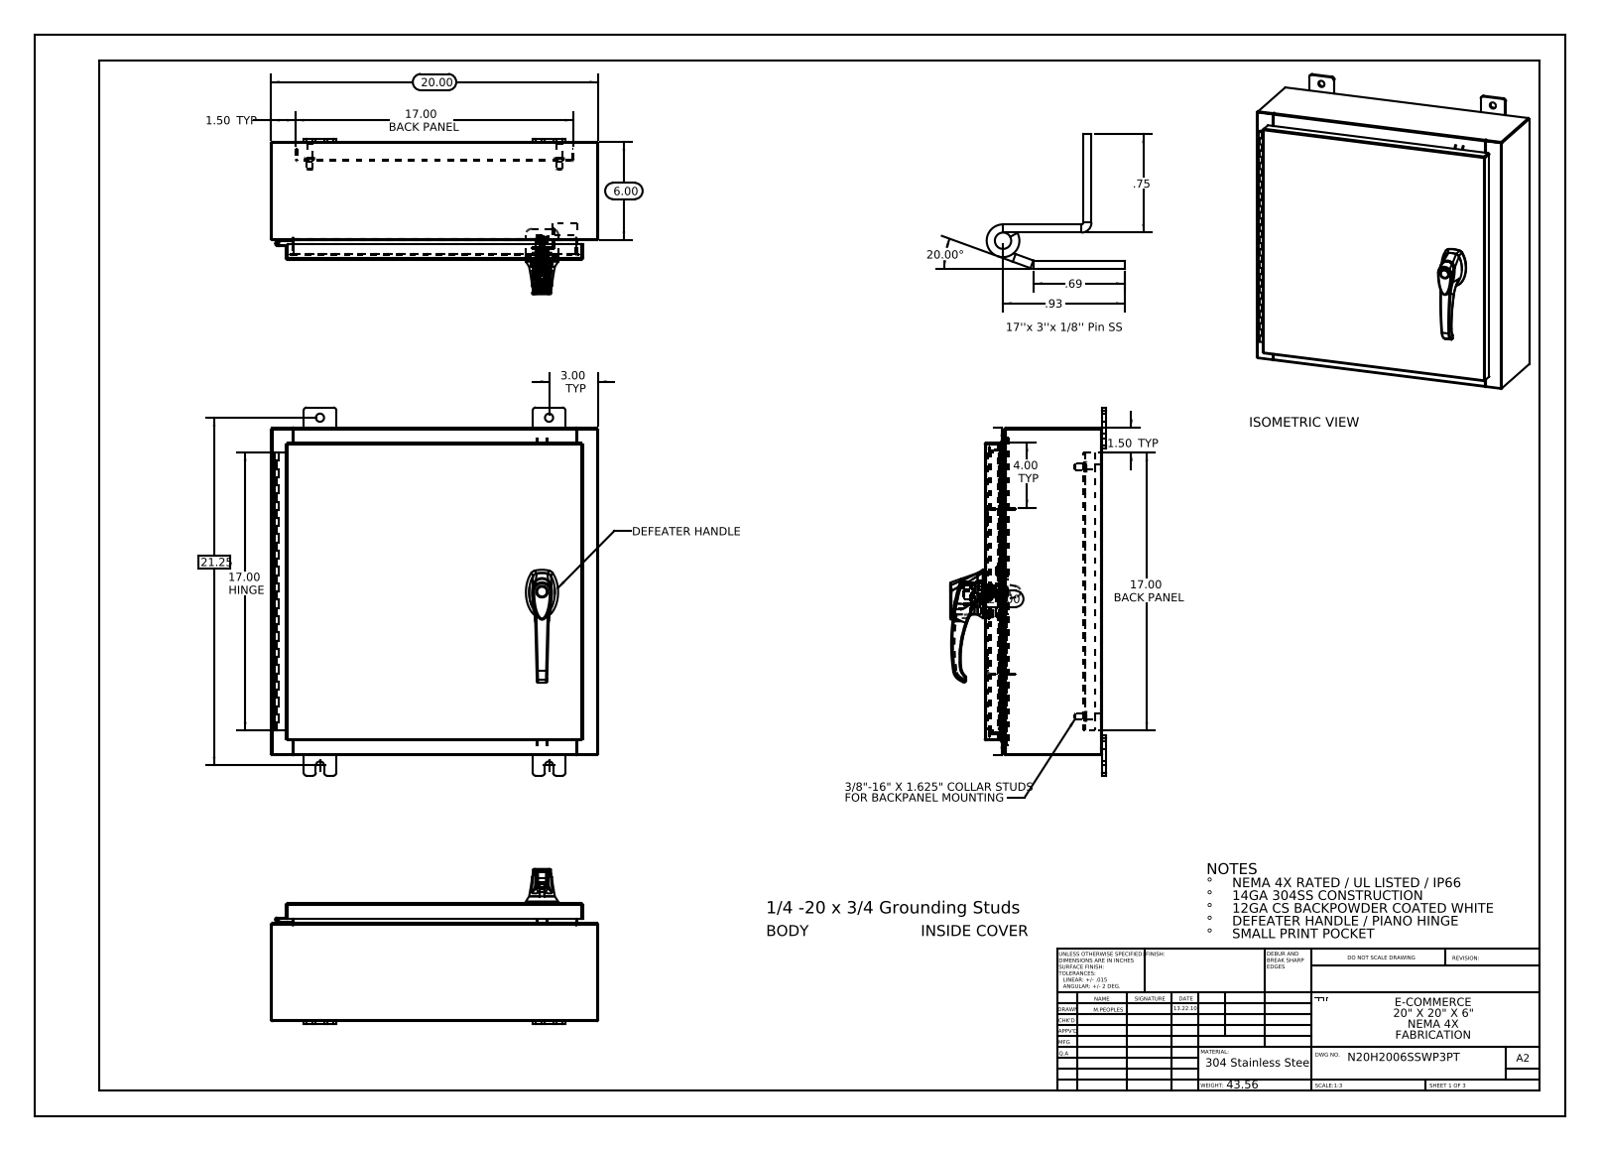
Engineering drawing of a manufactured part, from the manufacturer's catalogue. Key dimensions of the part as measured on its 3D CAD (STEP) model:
Part name (STEP PRODUCT): 297026; 26161102; N20H2006SSWP3PT Defeater Handle Rod; N20H2006SSWP3PT Hinge Enclosure Side2 (+8 more)
STEP written by: SolidWorks 2013 (CONFIG_CONTROL_DESIGN)
Units: inches
Bodies: 31 solids, 2316 faces (817 planar, 845 cylindrical, 654 other)
Overall size (bounding box): 22.5 × 20 × 9.495
Volume: 155.7 in³ · Surface area: 3 819 in²
Round holes (diameter × count): ⌀0.5 ×8, ⌀0.25 ×4, ⌀0.138 ×3, ⌀0.161 ×3, ⌀0.079 ×2, ⌀0.203 ×2, ⌀0.313 ×2, ⌀0.437 ×2, ⌀0.125 ×1, ⌀0.125 ×1, ⌀0.197 ×1, ⌀0.276 ×1
Round bosses / shafts (diameter × count): ⌀0.625 ×4, ⌀0.375 ×4, ⌀0.33 ×4, ⌀1.181 ×1, ⌀0.748 ×1, ⌀0.68 ×1, ⌀0.661 ×1, ⌀0.639 ×1
Partial cylindrical surfaces — rounded edges, fillets, slot ends (radius × count): R0.118 ×37, R0.006 ×33, R0.19 ×24, R0.013 ×22, R0.088 ×18, R0.039 ×15, R0.028 ×12, R0.008 ×6
Main face-to-face distances: 0.075, 7.126, 19.925, 7.051, 7.201, 0.104, 1, 1.075, 6.051, 6.126
Hole centre spacings: 3.404, 0.295, 0.625, 0.841, 1.25, 1.313, 1.561, 1.858
